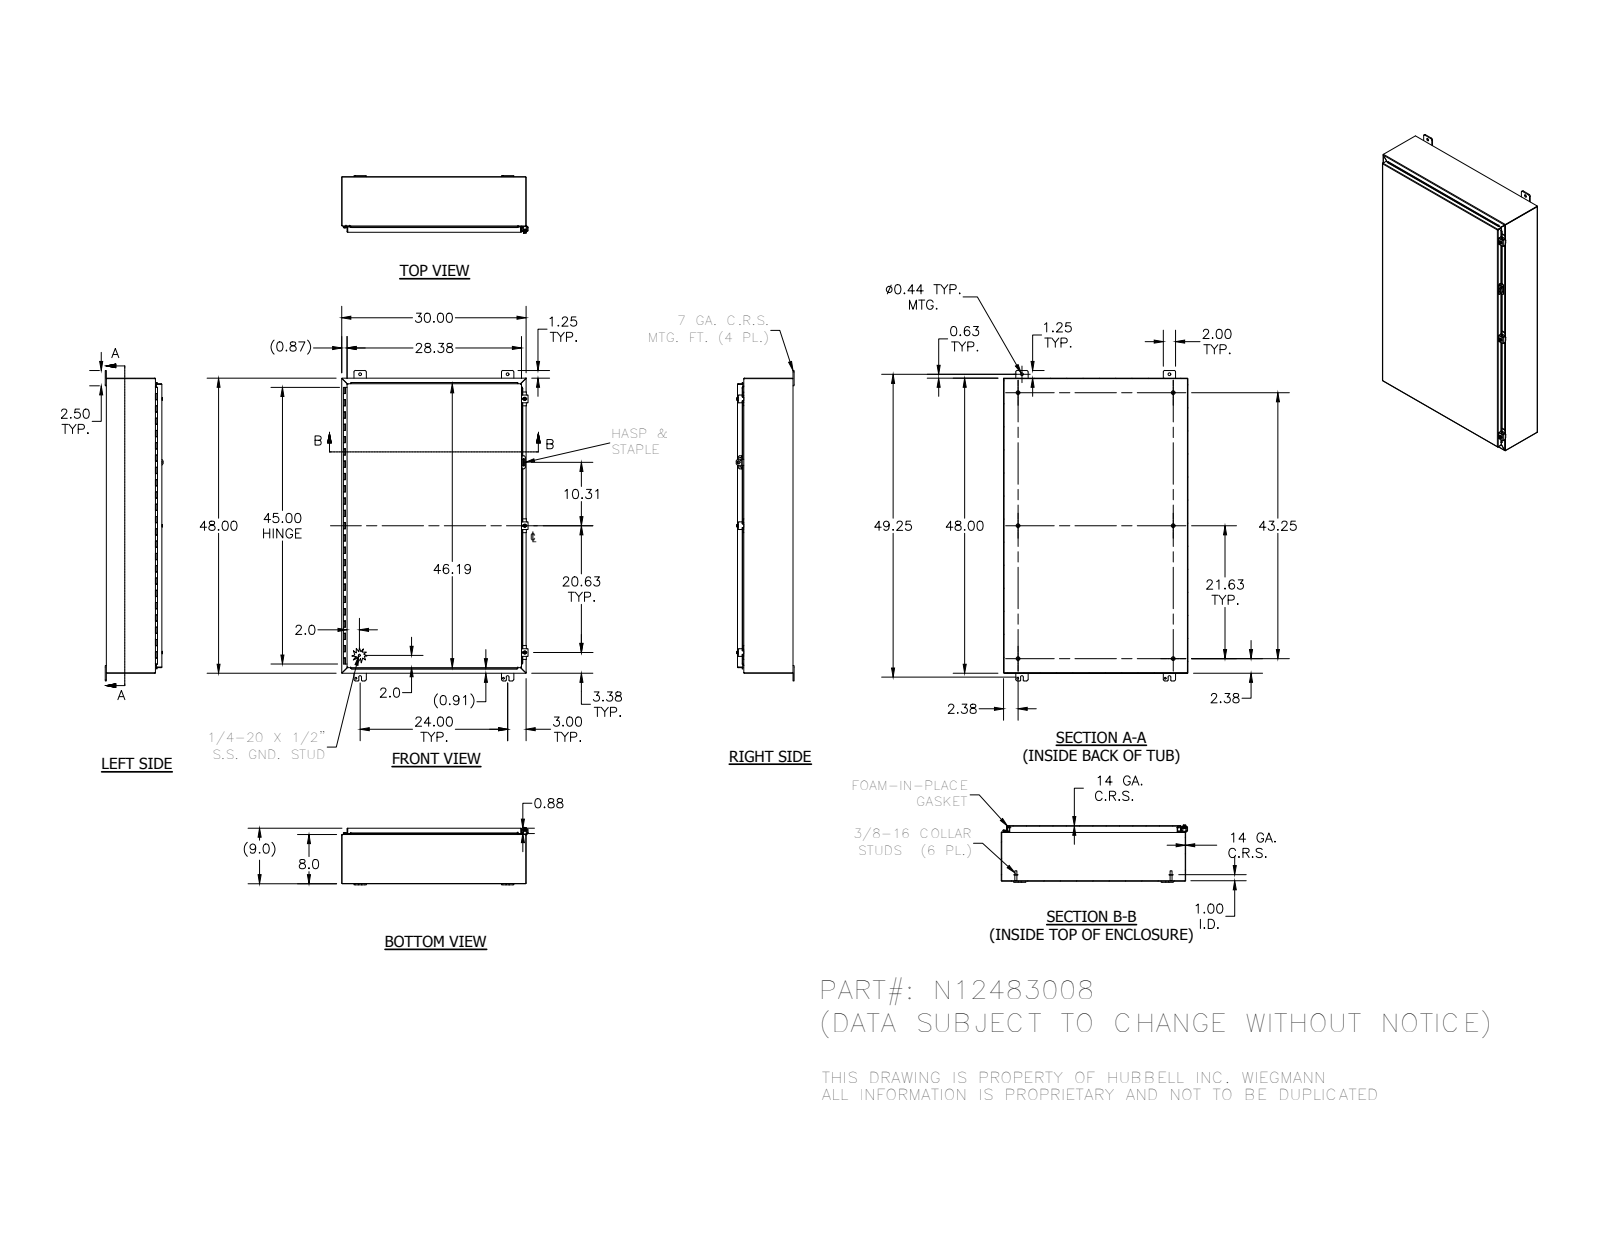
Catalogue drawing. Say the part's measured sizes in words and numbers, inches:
The part is named "N12483008; 34840; 38413; N123008TB (+8 more)". Its 3-D file was written by "Autodesk Inventor 2012 (AUTOMOTIVE_DESIGN)". It is 36 solids with 1233 faces: 726 planar, 386 cylindrical and 121 other. Overall it measures 50.5 by 30.311 by 9.41 inches. Its volume is 357 cubic inches and its surface area 9 431 square inches. Round holes: 4 of diameter 0.313, 4 of diameter 0.438, 3 of diameter 0.11, 3 of diameter 0.211, 3 of diameter 0.281, 3 of diameter 0.3, 1 of diameter 0.125, 1 of diameter 0.156, 1 of diameter 0.5. Round bosses or shafts: 6 of diameter 0.625, 6 of diameter 0.33, 5 of diameter 0.25, 3 of diameter 0.52, 3 of diameter 0.5, 3 of diameter 0.35, 1 of diameter 0.337, 1 of diameter 0.12. Partial cylindrical surfaces (rounded edges, fillets, slot ends): 39 of radius 0.03, 27 of radius 0.125, 27 of radius 0.25, 21 of radius 0.031, 21 of radius 0.105, 15 of radius 0.063, 6 of radius 0.1, 6 of radius 0.141. The main face-to-face distances are 0.074, 8.959, 8.885, 9.033, 29.926, 47.926, 7.926, 1.033, 29.852, 30. The hole center spacings are 1.593, 24, 48, 53.666, 0.791, 10.327, 23.357, 24.729.
